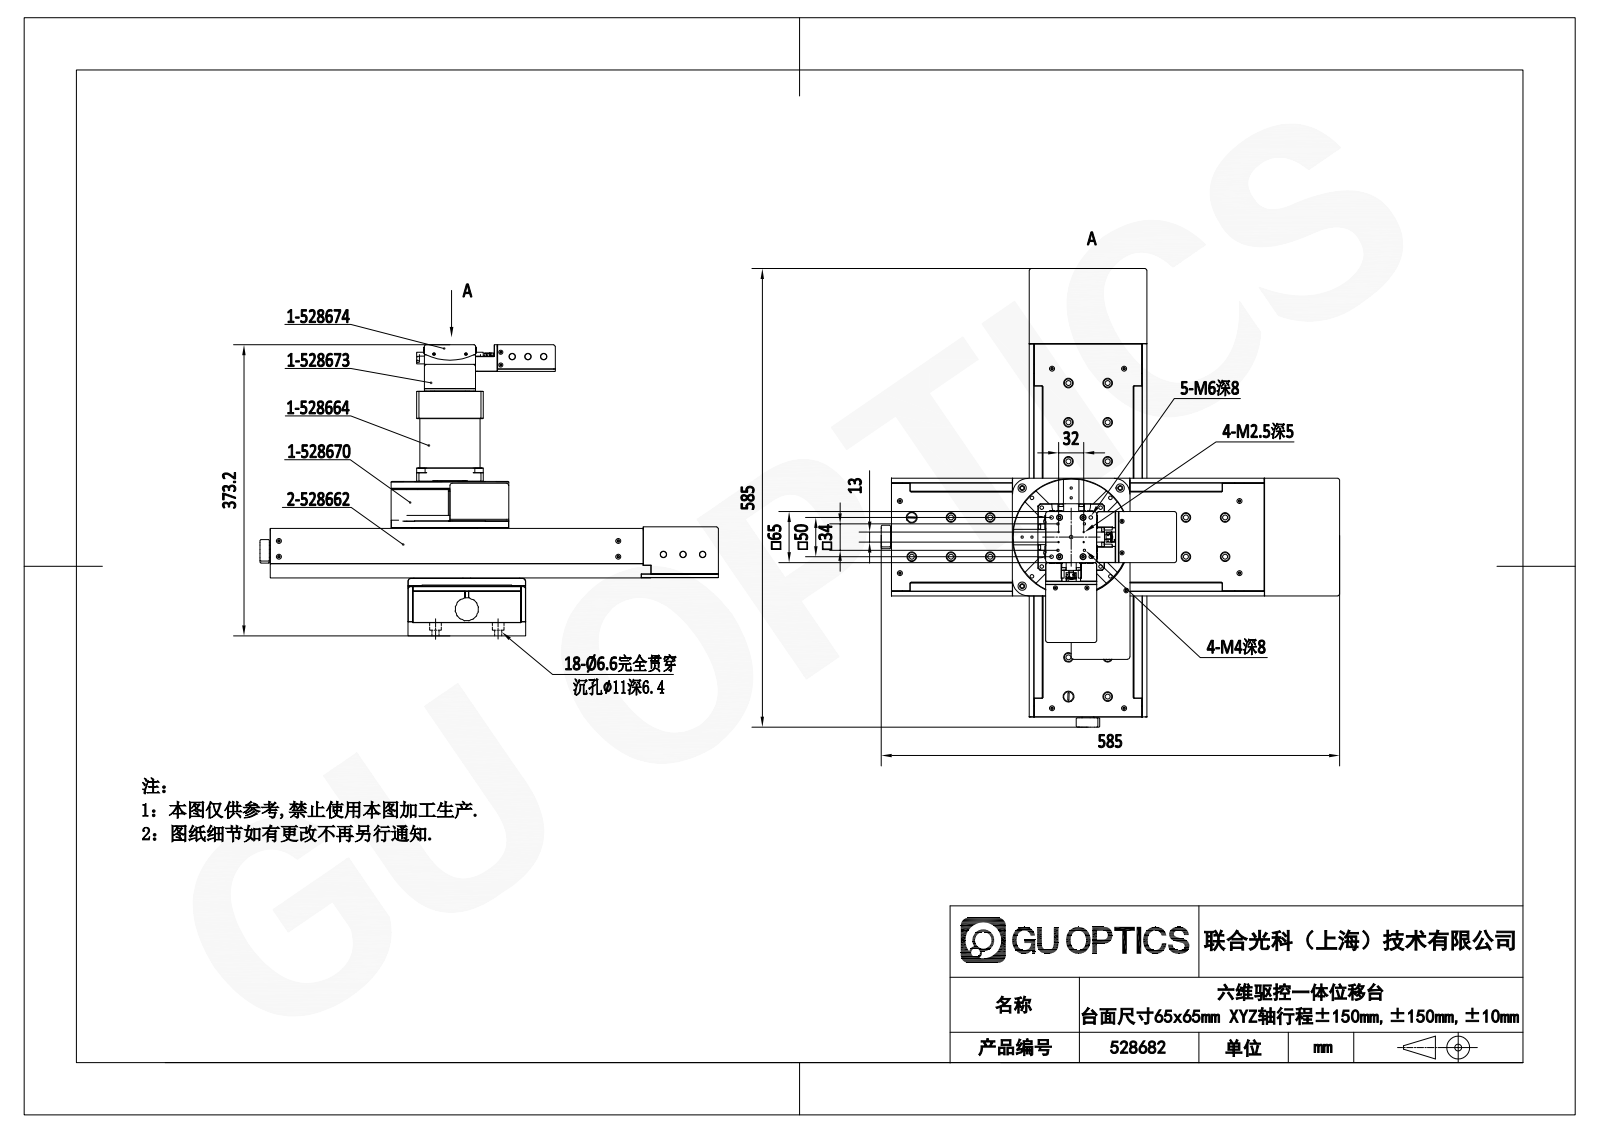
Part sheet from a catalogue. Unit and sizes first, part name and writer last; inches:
Units: inches
Overall size (bounding box): 23.031 × 23.031 × 14.623
Round holes (diameter × count): ⌀0.197 ×102, ⌀0.13 ×93, ⌀0.098 ×90, ⌀0.134 ×86, ⌀0.256 ×73, ⌀0.433 ×67, ⌀0.26 ×63, ⌀0.315 ×38, ⌀0.177 ×36, ⌀0.492 ×36, ⌀0.138 ×34, ⌀0.097 ×32
Round bosses / shafts (diameter × count): ⌀0.079 ×36, ⌀0.157 ×20, ⌀0.118 ×18, ⌀0.276 ×16, ⌀0.295 ×8, ⌀0.217 ×8, ⌀0.098 ×8, ⌀0.094 ×8
Partial cylindrical surfaces — rounded edges, fillets, slot ends (radius × count): R0.079 ×153, R0.039 ×57, R0.197 ×49, R0.118 ×35, R0.157 ×19, R0.295 ×18, R0.098 ×13, R0.053 ×8
Main face-to-face distances: 2.913, 0.236, 2.244, 1.535, 2.48, 0.709, 1.772, 0.669, 5.669, 5.906
Hole centre spacings: 0.492, 2.461, 0.984, 1.476, 1.969, 1.1, 1.556, 2.029
Volume: 483.6 in³ · Surface area: 3 503 in²
Bodies: 227 solids, 9469 faces (5718 planar, 2263 cylindrical, 1488 other)
Part name (STEP PRODUCT): 528662; 528664; 528674; 528670 (+2 more)
STEP written by: SolidWorks 2020 (CONFIG_CONTROL_DESIGN)
